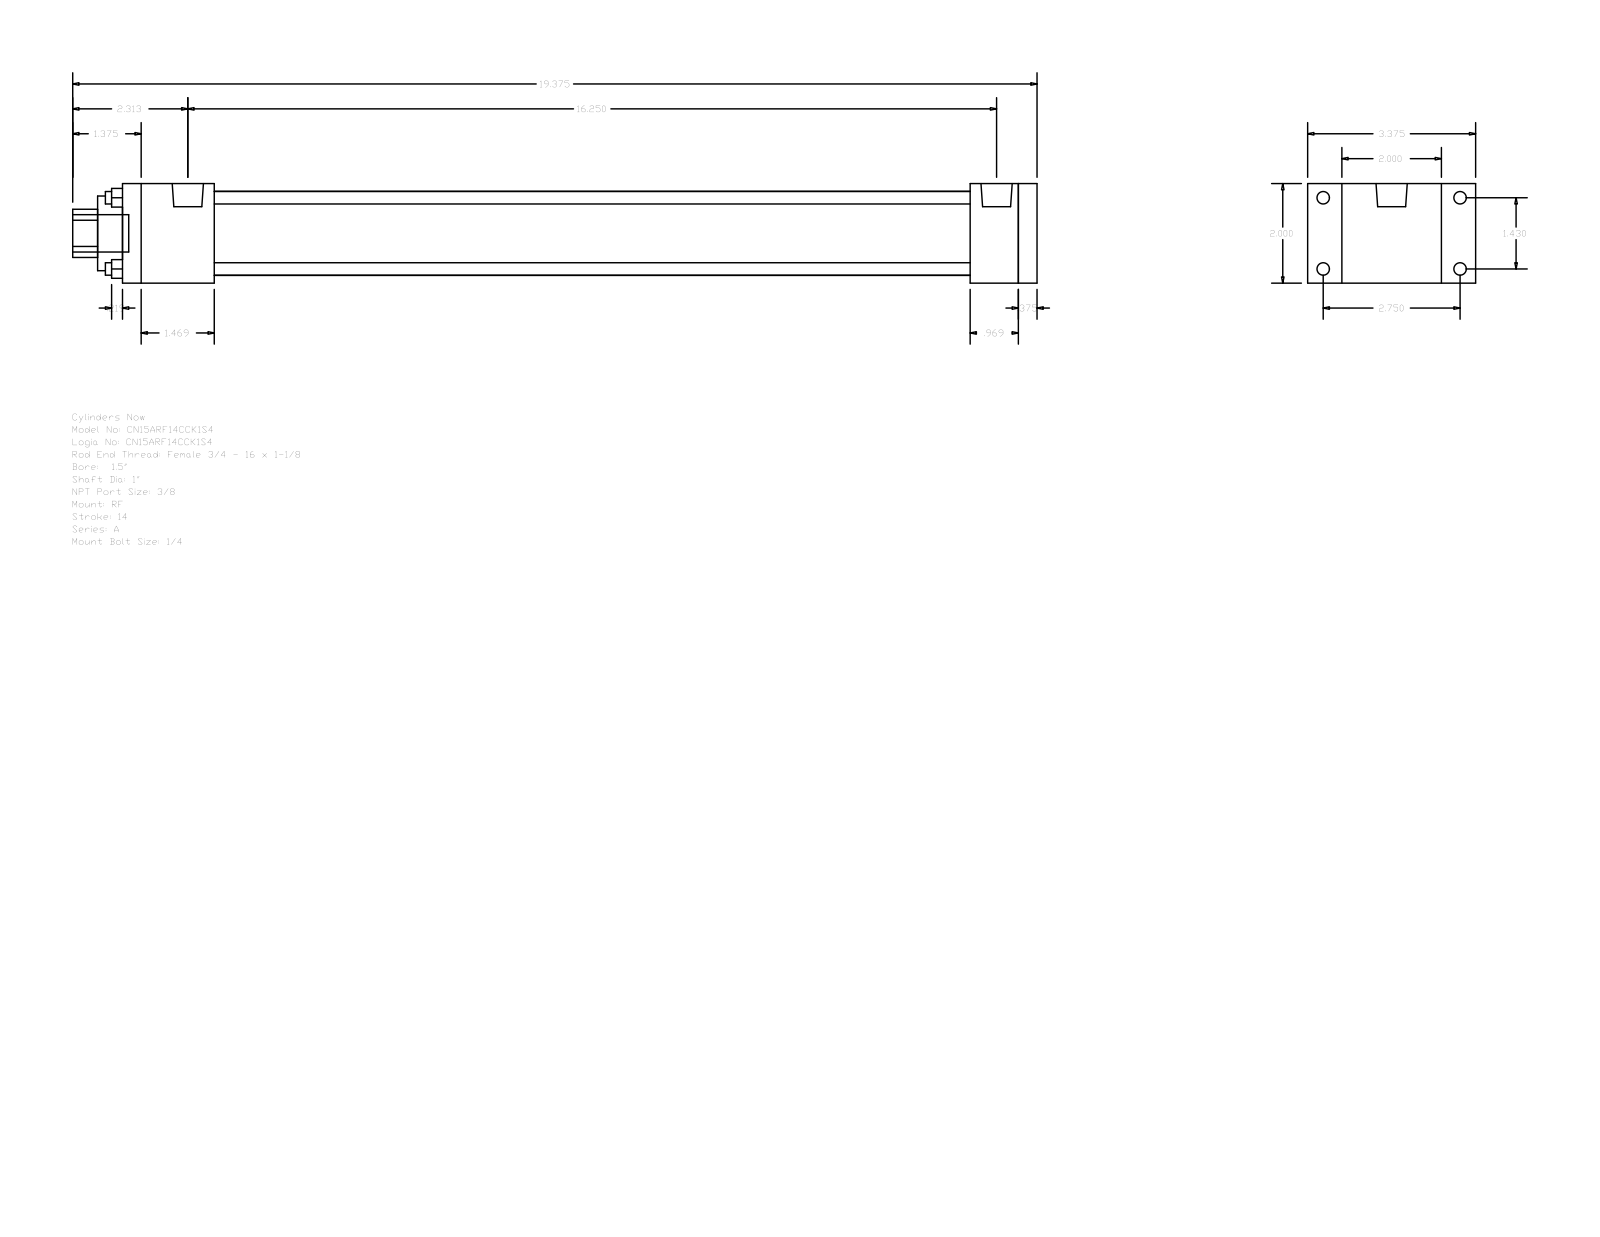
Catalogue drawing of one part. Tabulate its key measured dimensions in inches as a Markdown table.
| quantity | value |
| --- | --- |
| part name | A_RF__0150_1 |
| STEP written by | GSSL Pune (CONFIG_CONTROL_DESIGN) |
| units | inches |
| bodies | 0 solids, 92 faces (64 planar, 28 cylindrical, 0 other) |
| overall size | 19.375 × 3.375 × 2 |
| round holes (diameter × count) | 0.25 × 4, 1 × 1, 1.5 × 1, 1.69 × 1 |
| round bosses / shafts (diameter × count) | 0.25 × 4, 0.219 × 4, 0.627 × 2, 0.75 × 1 |
| partial cylindrical surfaces (radius × count) | 0.484 × 1 |
| main face-to-face distances | 2, 0.375, 18, 18.375, 17.031, 0.969, 1.344, 1.844, 15.187, 16.156 |
| hole center spacings | 1.011, 1.43, 2.022 |
